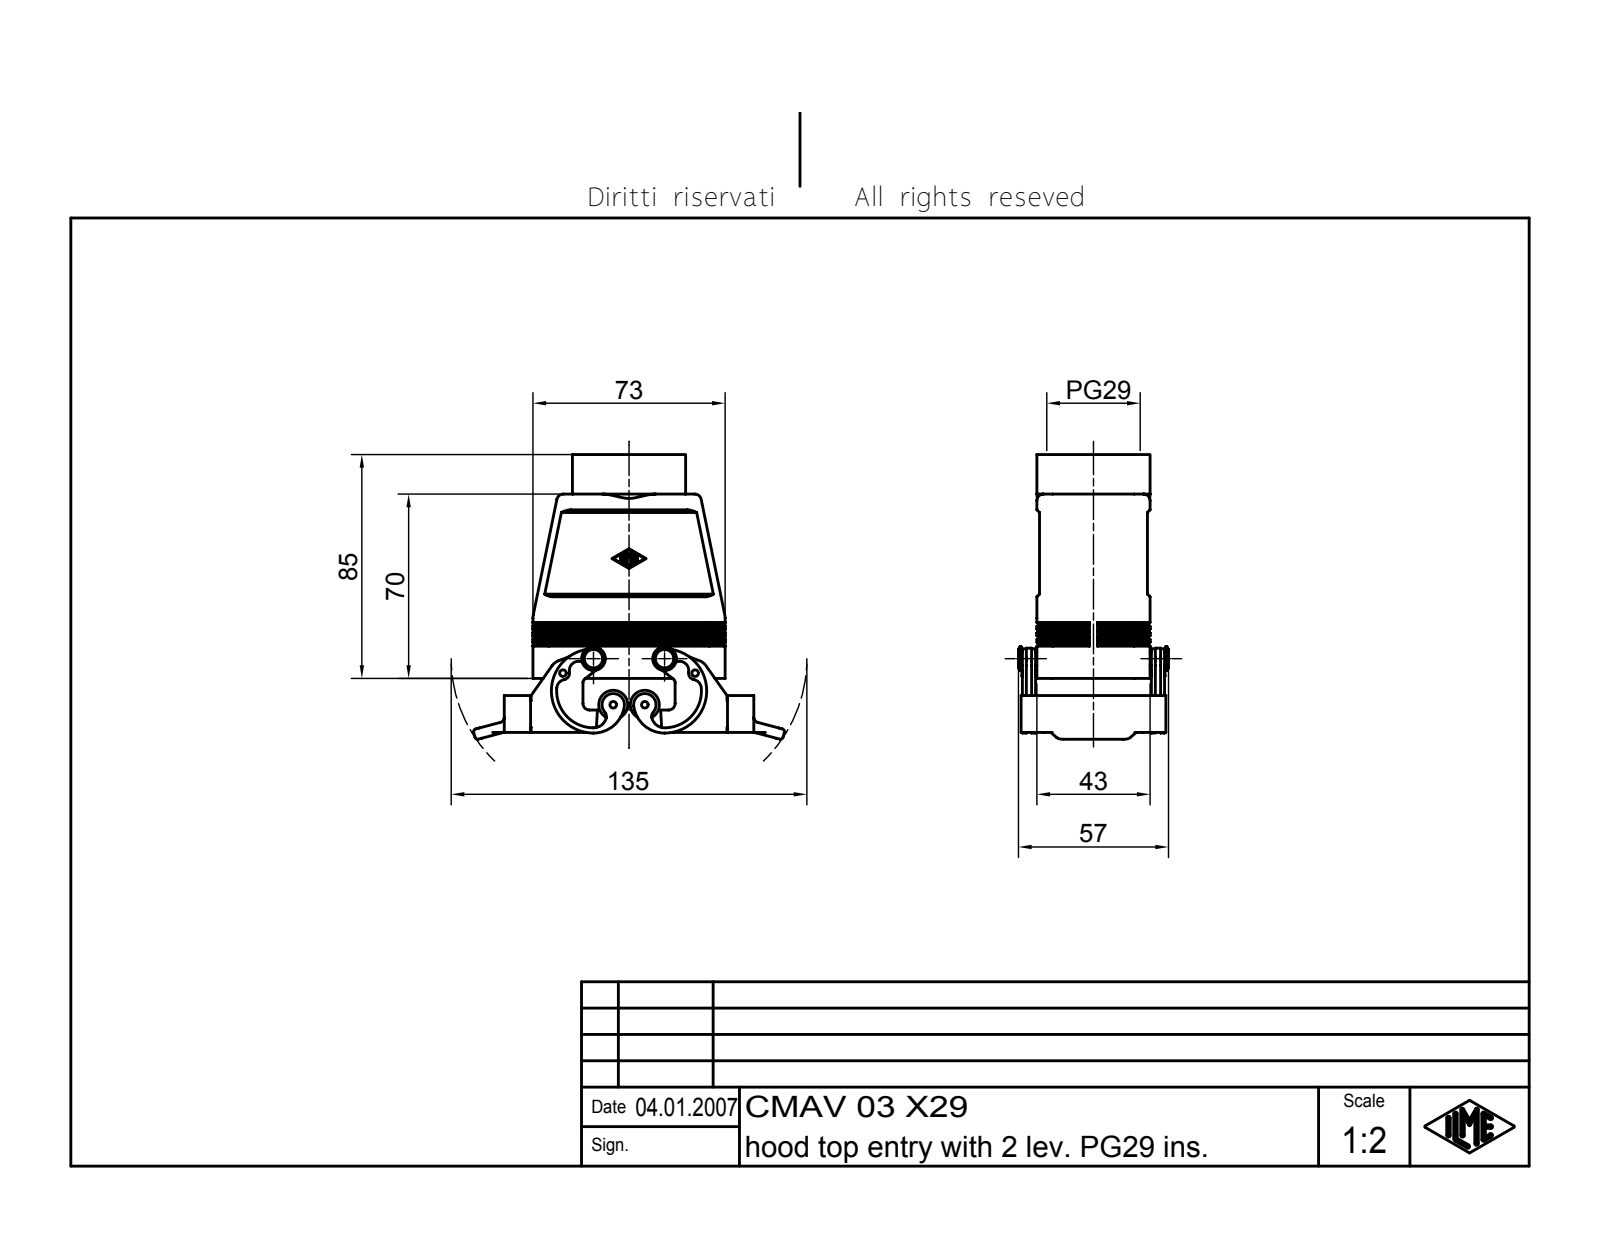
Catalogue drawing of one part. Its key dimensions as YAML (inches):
part_name: "CAV Tüllengehäuse 2 Bügel für einen Einsatz Teil A"
step_written_by: "Autodesk Inventor 7 (AUTOMOTIVE_DESIGN)"
units: inches
bodies: {solids: 1, faces: 847, planar: 248, cylindrical: 230, other: 369}
overall_size: [4.649, 4.256, 2.244]
volume: 4.998
surface_area: 80.76
round_holes:
  - {diameter: 0.098, count: 2}
  - {diameter: 1.318, count: 1}
  - {diameter: 1.397, count: 1}
round_bosses_or_shafts:
  - {diameter: 0.433, count: 2}
  - {diameter: 0.354, count: 2}
  - {diameter: 0.197, count: 2}
  - {diameter: 0.079, count: 2}
  - {diameter: 1.693, count: 1}
  - {diameter: 1.357, count: 1}
partial_cylinders:
  - {radius: 0.01, count: 14}
  - {radius: 0.039, count: 12}
  - {radius: 0.079, count: 10}
  - {radius: 0.098, count: 10}
  - {radius: 0.236, count: 10}
  - {radius: 0.118, count: 8}
  - {radius: 0.138, count: 4}
  - {radius: 0.197, count: 4}
face_to_face_distances: [0.079, 0.118, 1.654, 1.575, 0.197, 1.457, 0.157, 1.535, 0.039, 0.354]
hole_center_spacings: [1.976]
